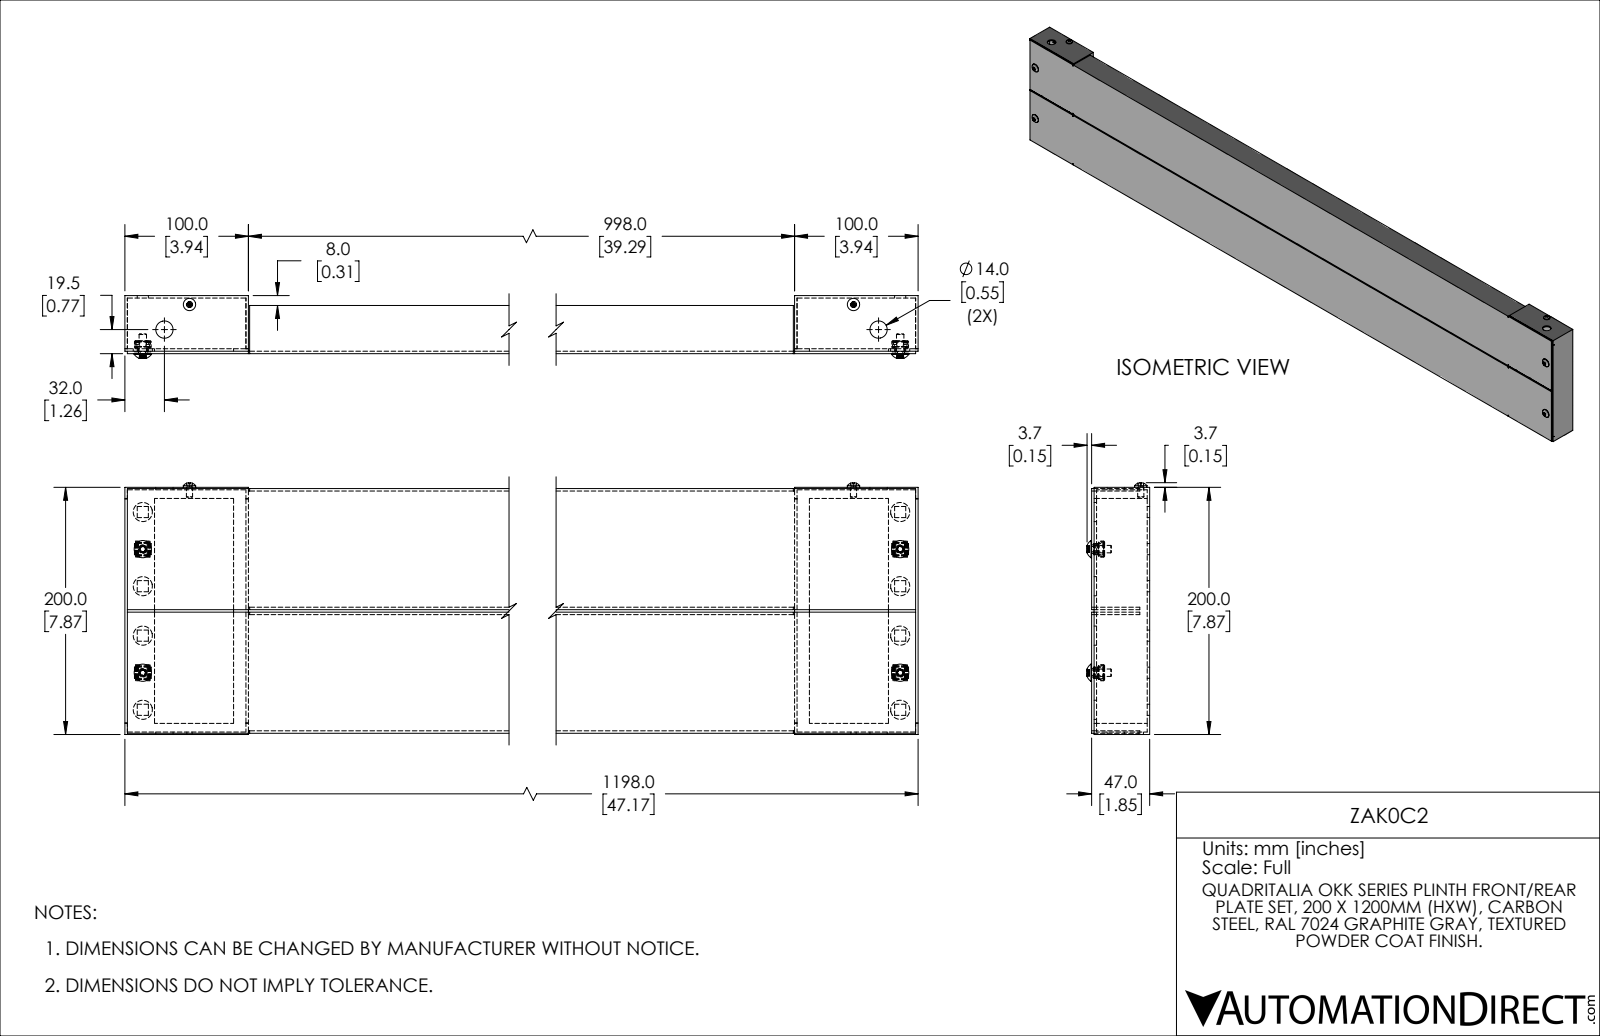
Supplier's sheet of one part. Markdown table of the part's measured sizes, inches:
| quantity | value |
| --- | --- |
| part name | ZAK0C2 |
| STEP written by | SolidWorks 2021 (CONFIG_CONTROL_DESIGN) |
| units | inches |
| bodies | 18 solids, 760 faces (488 planar, 248 cylindrical, 24 other) |
| overall size | 47.165 × 8.021 × 1.996 |
| volume | 59.34 in³ |
| surface area | 1 535 in² |
| round holes (diameter × count) | 0.61 × 8, 0.276 × 4, 0.167 × 2, 0.194 × 2, 0.194 × 2, 0.551 × 2 |
| round bosses / shafts (diameter × count) | 0.551 × 4, 0.236 × 4, 0.394 × 2, 0.197 × 2 |
| partial cylindrical surfaces (radius × count) | 0.02 × 68, 0.01 × 48, 0.039 × 20 |
| main face-to-face distances | 0.079, 3.858, 3.937, 3.78, 0.157, 7.717, 1.772, 3.701, 4.016, 7.795 |
| hole center spacings | 1.181, 46.039, 3.937, 46.024, 46.192, 2.362, 2.756, 5.118 |
